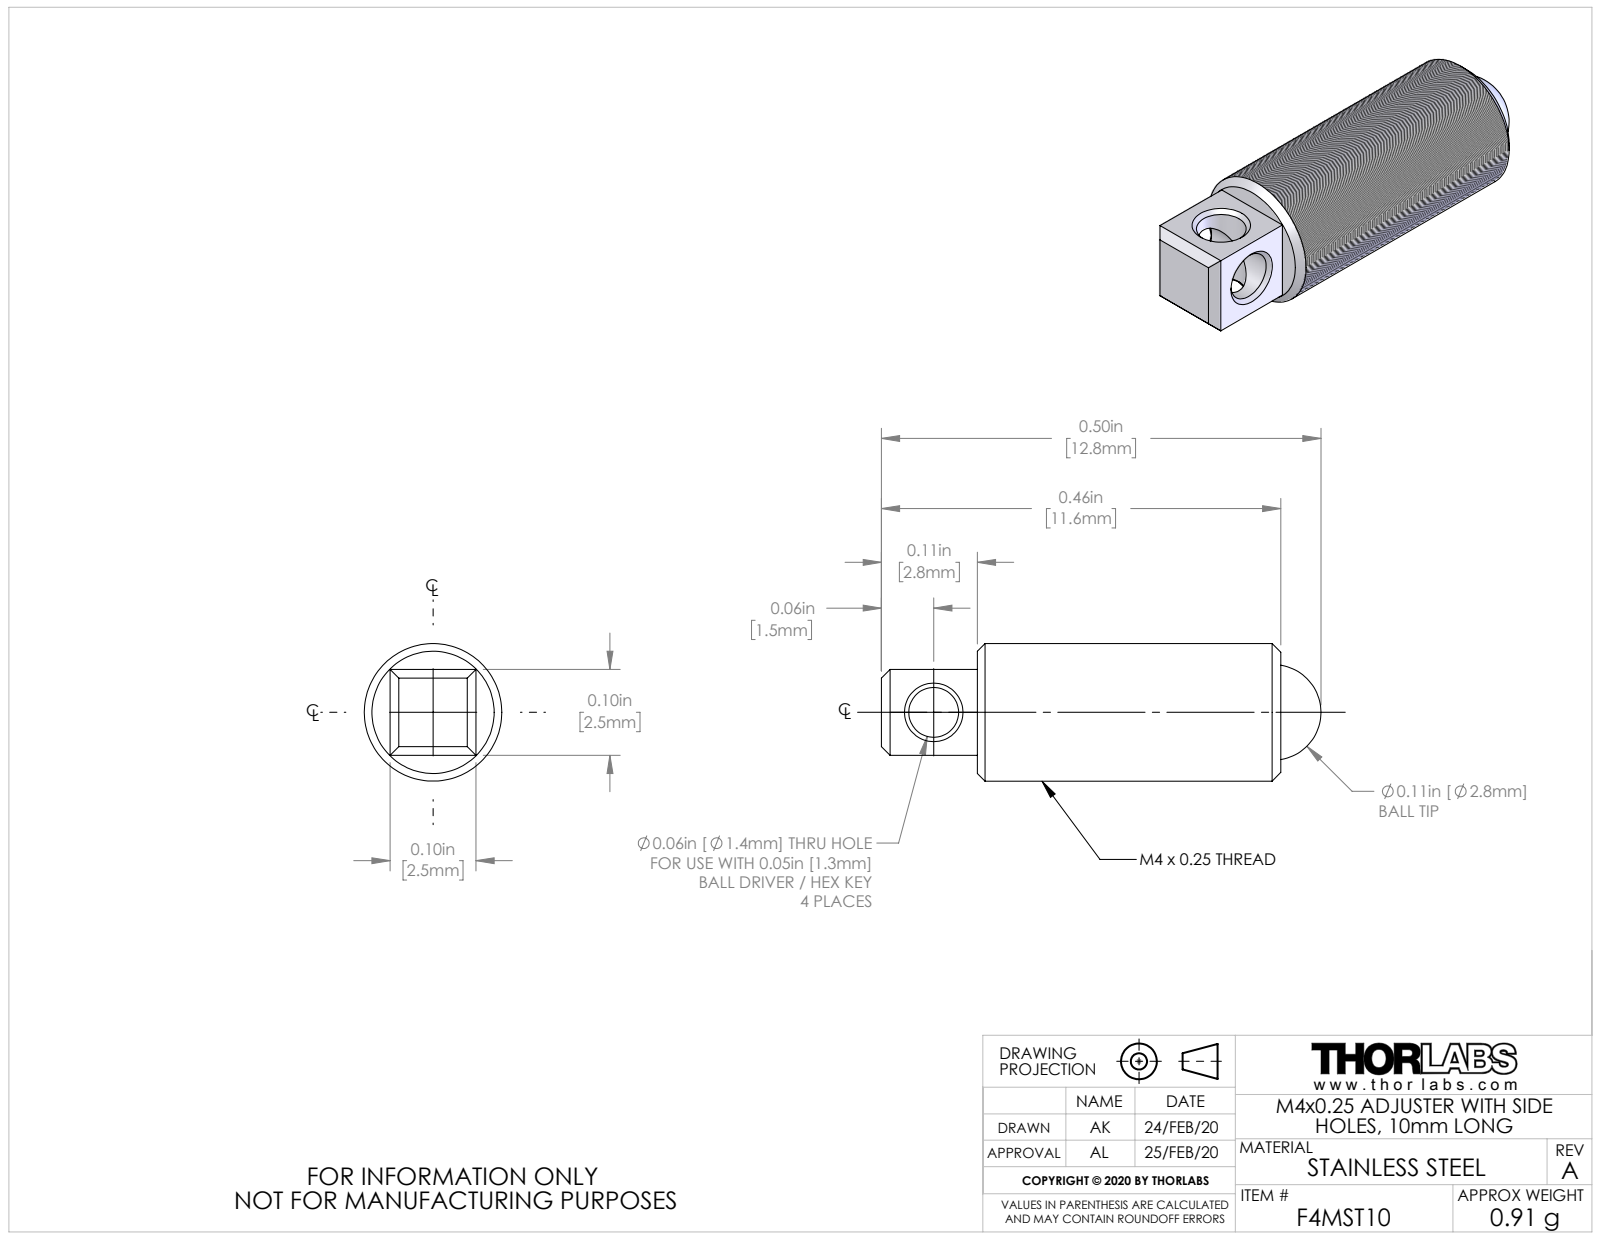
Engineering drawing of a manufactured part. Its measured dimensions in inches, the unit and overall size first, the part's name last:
Units: inches
Overall size (bounding box): 0.504 × 0.157 × 0.157
Round holes (diameter × count): ⌀0.057 ×2, ⌀0.11 ×1
Round bosses / shafts (diameter × count): ⌀0.157 ×1
Main face-to-face distances: 0.098, 0.11, 0.348, 0.458
Volume: 0.008 in³ · Surface area: 0.308 in²
Bodies: 2 solids, 41 faces (11 planar, 12 cylindrical, 18 other)
Part name (STEP PRODUCT): TTN203596-E0W
STEP written by: SolidWorks 2018 (AUTOMOTIVE_DESIGN)
